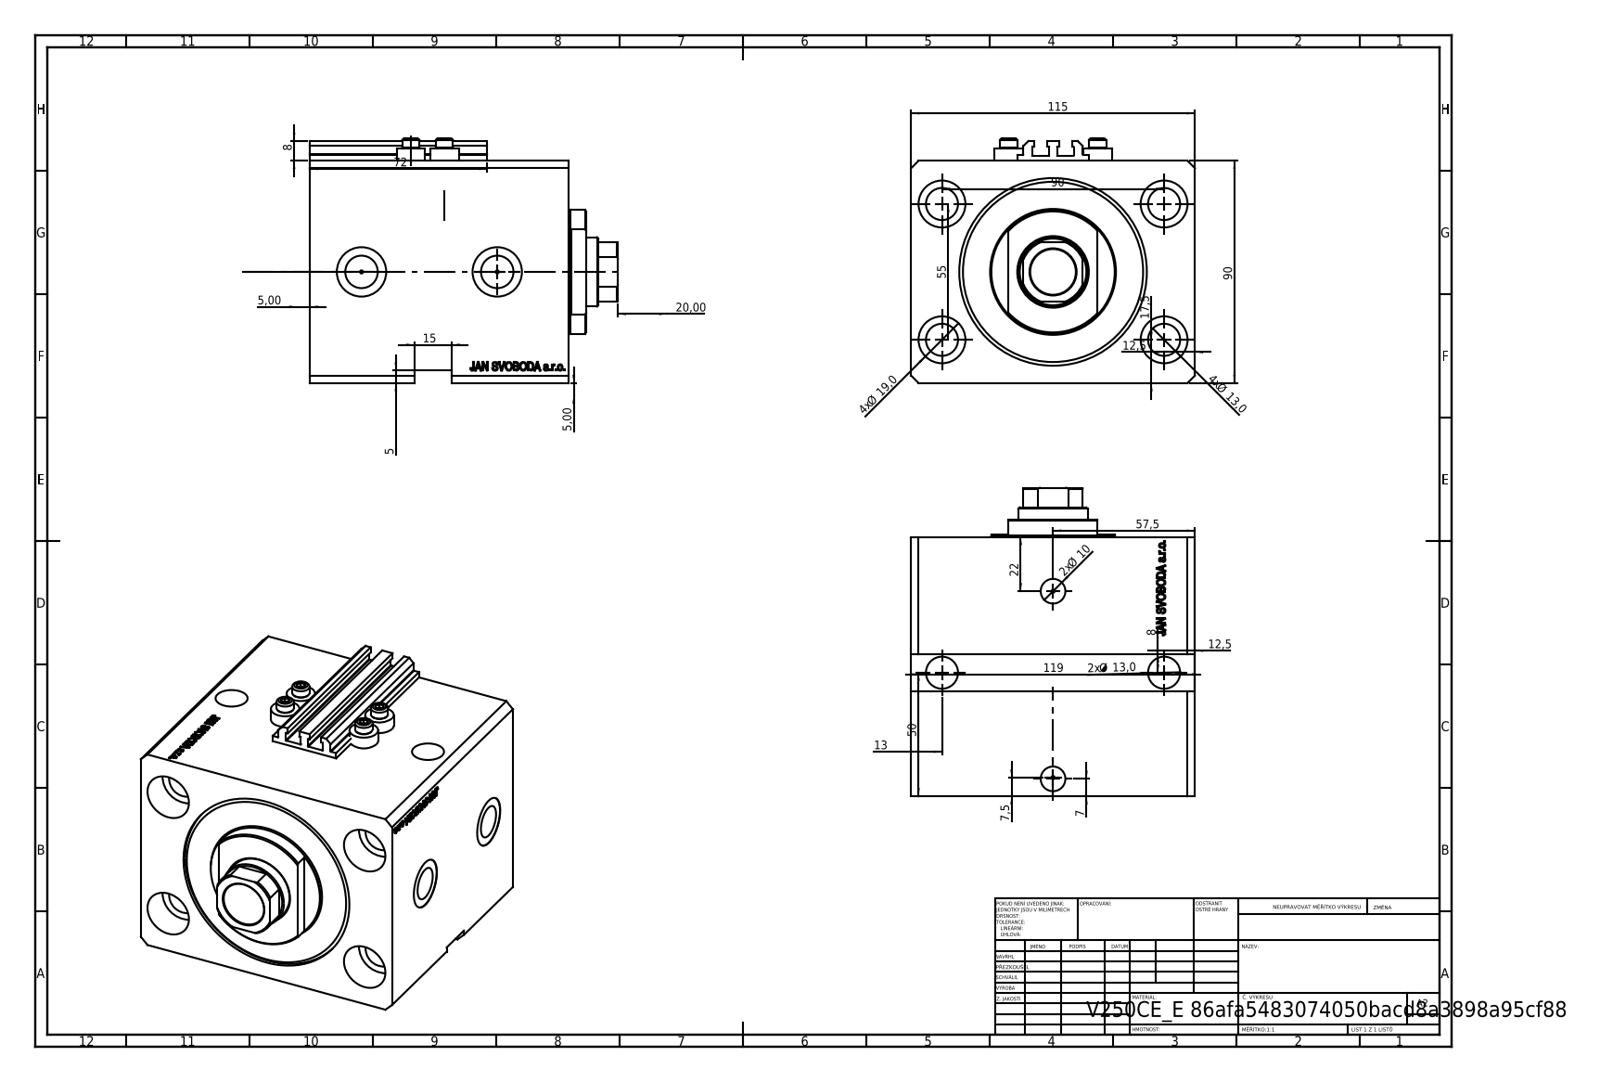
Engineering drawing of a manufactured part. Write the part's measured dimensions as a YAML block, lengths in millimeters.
part_name: "V250CE_VC_E; V250CE_E_Body; ALLEN BOLT V250CE; V250CE_C_VCP"
step_written_by: "SolidWorks 2019 (CONFIG_CONTROL_DESIGN)"
units: millimeters
bodies: {solids: 8, faces: 1123, planar: 547, cylindrical: 138, other: 438}
overall_size: [124.9, 115, 99]
volume: 950900
surface_area: 157650
round_holes:
  - {diameter: 13, count: 6}
  - {diameter: 1.25, count: 4}
  - {diameter: 4, count: 4}
  - {diameter: 19, count: 4}
  - {diameter: 10, count: 2}
  - {diameter: 13.16, count: 2}
  - {diameter: 20, count: 2}
  - {diameter: 18.5, count: 1}
  - {diameter: 28, count: 1}
  - {diameter: 63, count: 1}
  - {diameter: 76, count: 1}
round_bosses_or_shafts:
  - {diameter: 11.6, count: 4}
  - {diameter: 7, count: 4}
  - {diameter: 50, count: 1}
partial_cylinders:
  - {radius: 0.2, count: 10}
  - {radius: 13.5, count: 1}
face_to_face_distances: [90, 115, 105, 87.1, 17.9, 57, 74.9, 30.1, 20, 54.9]
hole_center_spacings: [52.74, 55, 90, 13.6, 27.39, 28.46, 33.62, 36]
